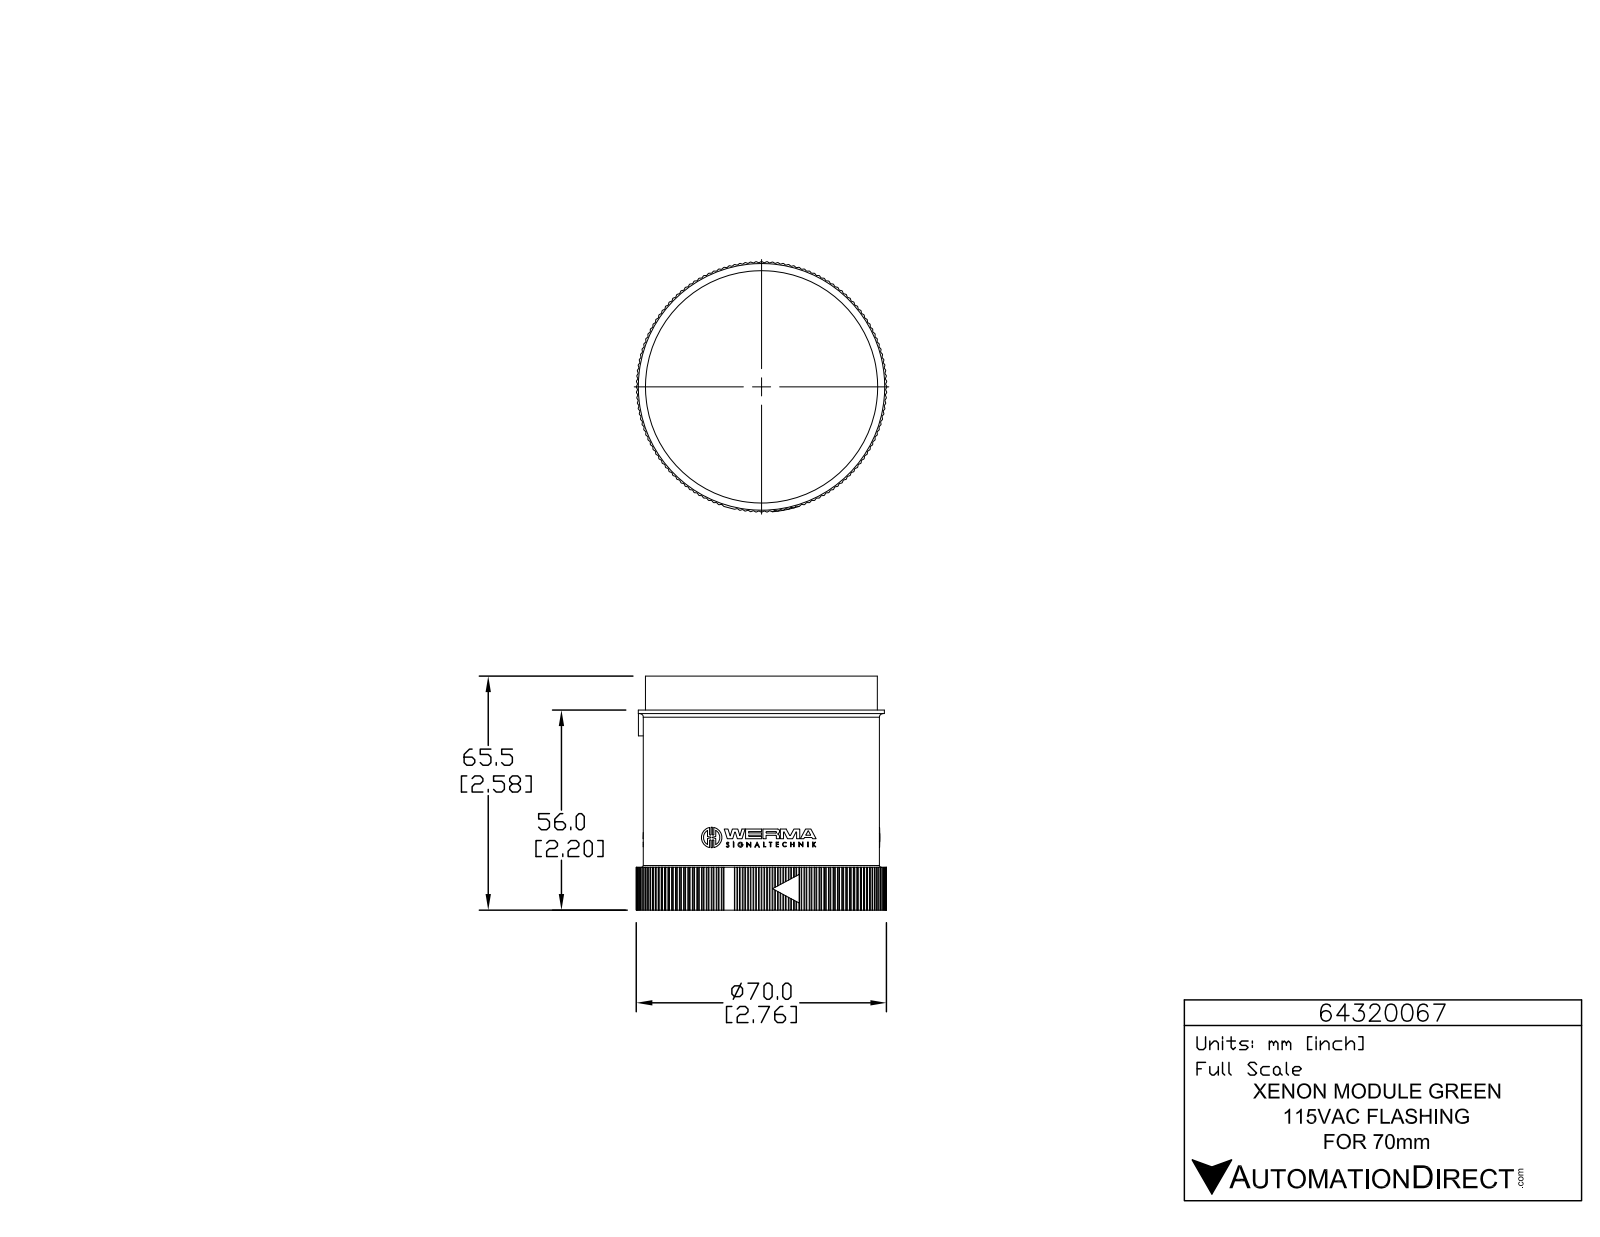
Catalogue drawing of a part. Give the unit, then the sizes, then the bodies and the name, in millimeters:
Units: millimetres
Overall size (bounding box): 70.2 × 70.2 × 65.5
Round holes (diameter × count): ⌀1 ×3, ⌀65.4 ×1
Round bosses / shafts (diameter × count): ⌀5.7 ×3, ⌀1.4 ×3, ⌀69 ×1, ⌀66.2 ×1, ⌀65 ×1
Partial cylindrical surfaces — rounded edges, fillets, slot ends (radius × count): R0.2 ×285, R0.2 ×6, R0.2 ×6, R0.2 ×6, R3.3 ×6, R0.1 ×3, R0.1 ×3, R0.2 ×3
Main face-to-face distances: 55.9, 62.3, 9.6, 65.5, 56, 46.4, 9.5, 62.3, 12, 2.4
Volume: 197 000 mm³ · Surface area: 24 180 mm²
Bodies: 1 solid, 1400 faces (832 planar, 563 cylindrical, 5 other)
Part name (STEP PRODUCT): 64320067
STEP written by: SolidWorks 2015 (AUTOMOTIVE_DESIGN)
